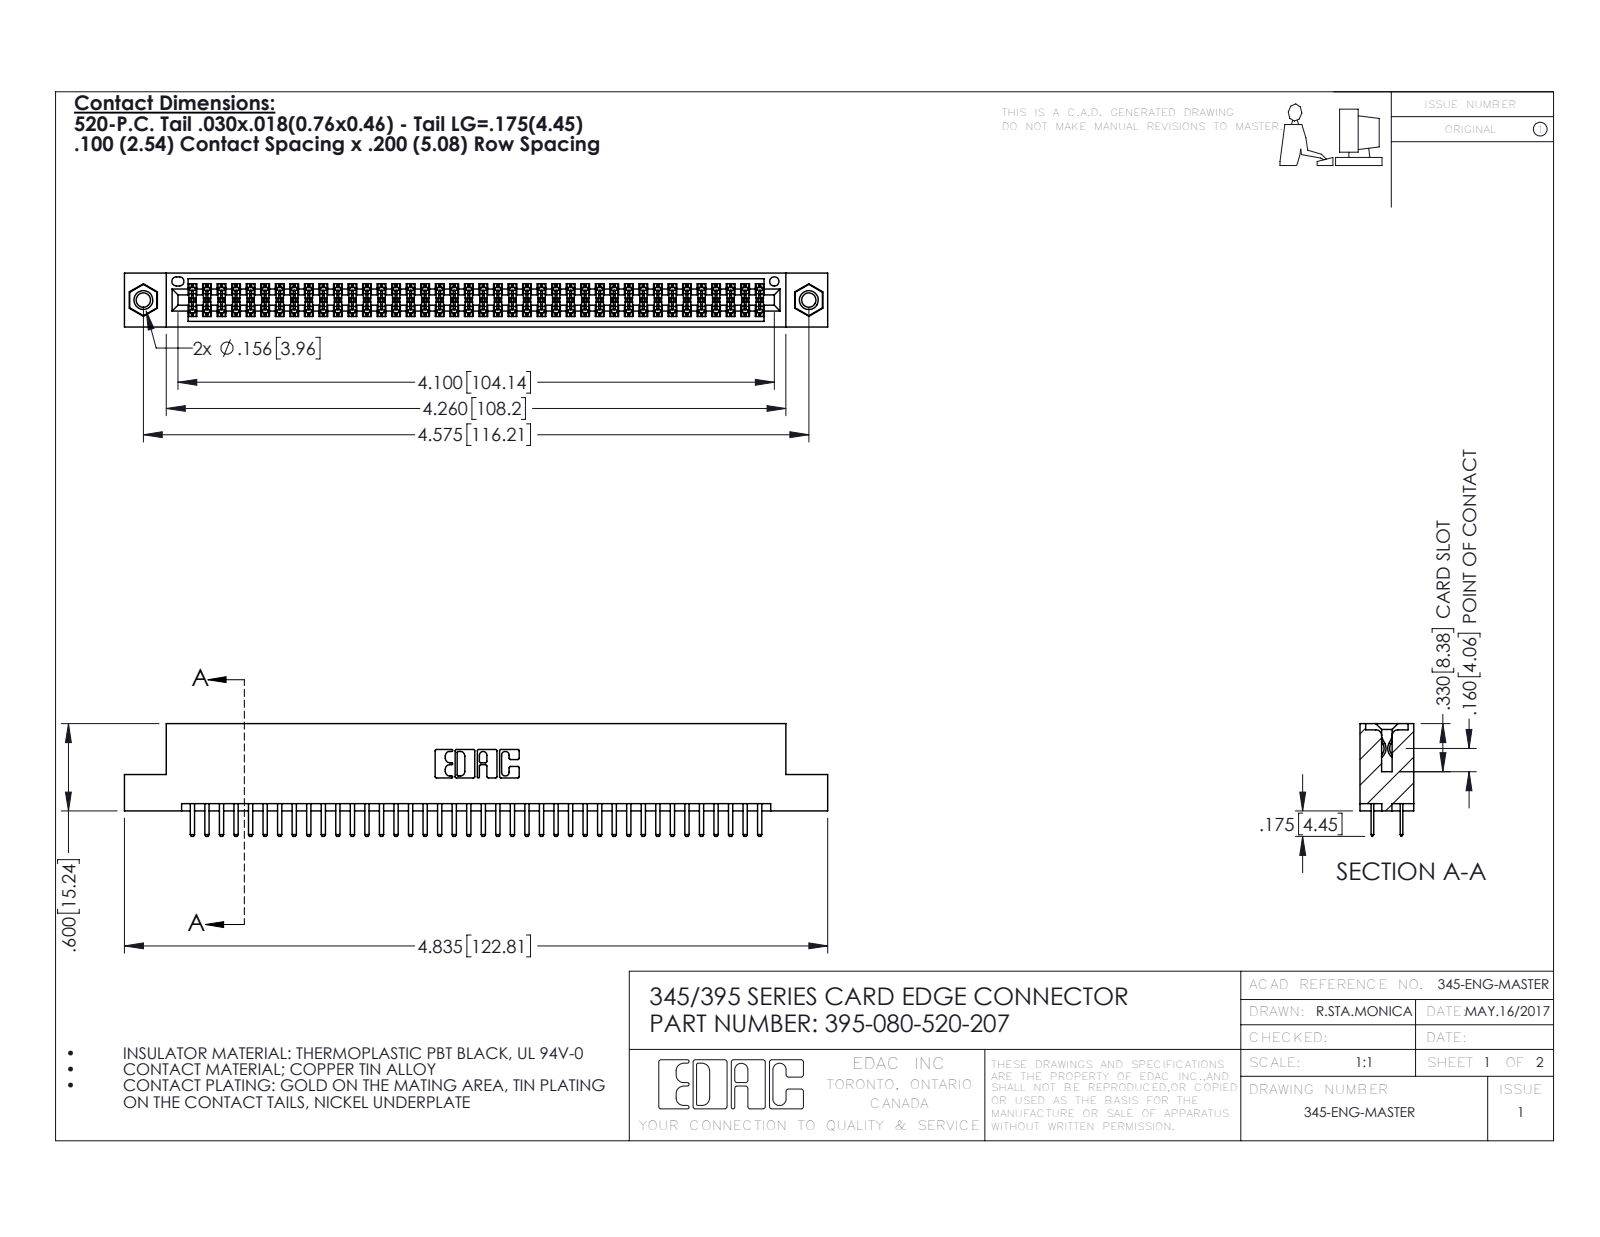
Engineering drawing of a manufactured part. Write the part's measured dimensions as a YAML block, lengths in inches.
part_name: "345-250-001_345-250-005-103; 345 Part_Flush Mounting Lugs - 0.156 Dia-TI; 395-080-520-207; 345-292-001_345-293-120"
step_written_by: "SolidWorks 2016 (CONFIG_CONTROL_DESIGN)"
units: inches
bodies: {solids: 83, faces: 4506, planar: 2912, cylindrical: 1578, other: 16}
overall_size: [4.835, 0.775, 0.37]
volume: 0.724
surface_area: 27.05
round_holes:
  - {diameter: 0.098, count: 2}
  - {diameter: 0.125, count: 2}
  - {diameter: 0.156, count: 2}
  - {diameter: 0.064, count: 1}
round_bosses_or_shafts:
  - {diameter: 0.155, count: 2}
partial_cylinders:
  - {radius: 0.006, count: 120}
  - {radius: 0.01, count: 84}
  - {radius: 0.01, count: 22}
  - {radius: 0.007, count: 6}
  - {radius: 0.031, count: 6}
  - {radius: 0.026, count: 3}
  - {radius: 0.014, count: 2}
  - {radius: 0.019, count: 2}
face_to_face_distances: [0.072, 0.298, 0.2, 0.37, 0.098, 0.272, 0.025, 0.225, 0.022, 0.072]
hole_center_spacings: [0.27, 4.339, 4.575]
